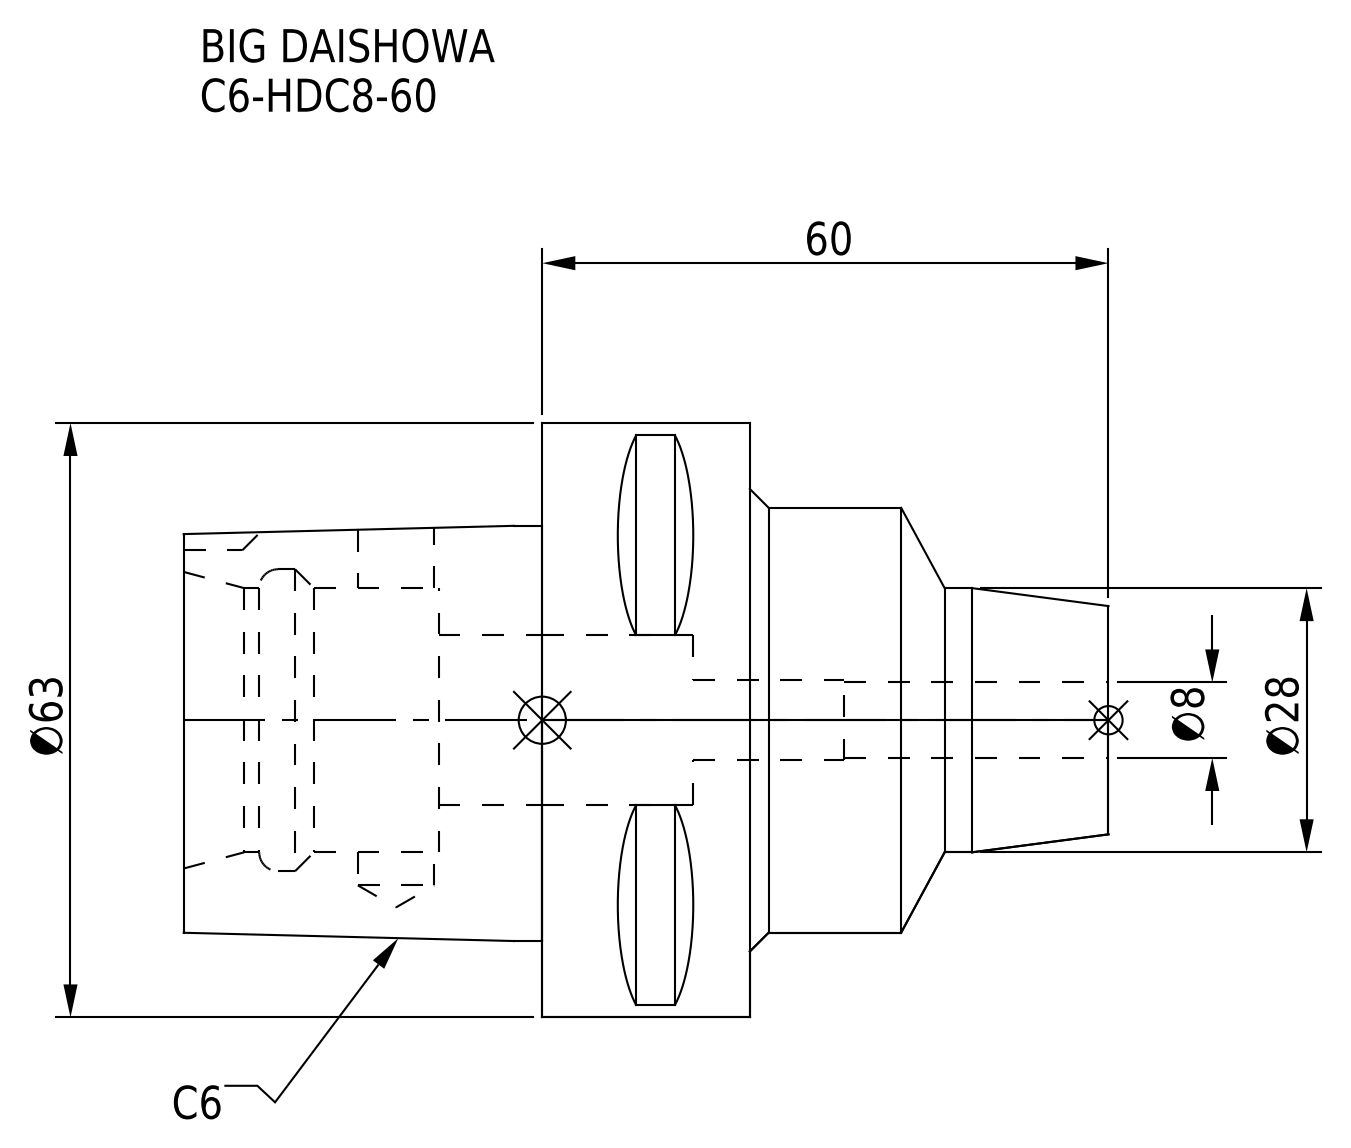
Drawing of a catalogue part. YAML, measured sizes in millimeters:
part_name: "C6-HDC8-60"
step_written_by: "CREO PARAMETRIC BY PTC INC, 2016380 (AUTOMOTIVE_DESIGN)"
units: millimeters
bodies: {solids: 1, faces: 68, planar: 29, cylindrical: 23, other: 16}
overall_size: [98, 63, 63]
volume: 134499
surface_area: 24715
round_holes:
  - {diameter: 8, count: 1}
  - {diameter: 8.1, count: 1}
  - {diameter: 8.5, count: 1}
  - {diameter: 18, count: 1}
  - {diameter: 28, count: 1}
  - {diameter: 32, count: 1}
round_bosses_or_shafts:
  - {diameter: 63, count: 1}
  - {diameter: 45, count: 1}
partial_cylinders:
  - {radius: 5, count: 1}
face_to_face_distances: [22, 38, 60, 27, 98, 71, 33, 11, 24.89, 55.4]
